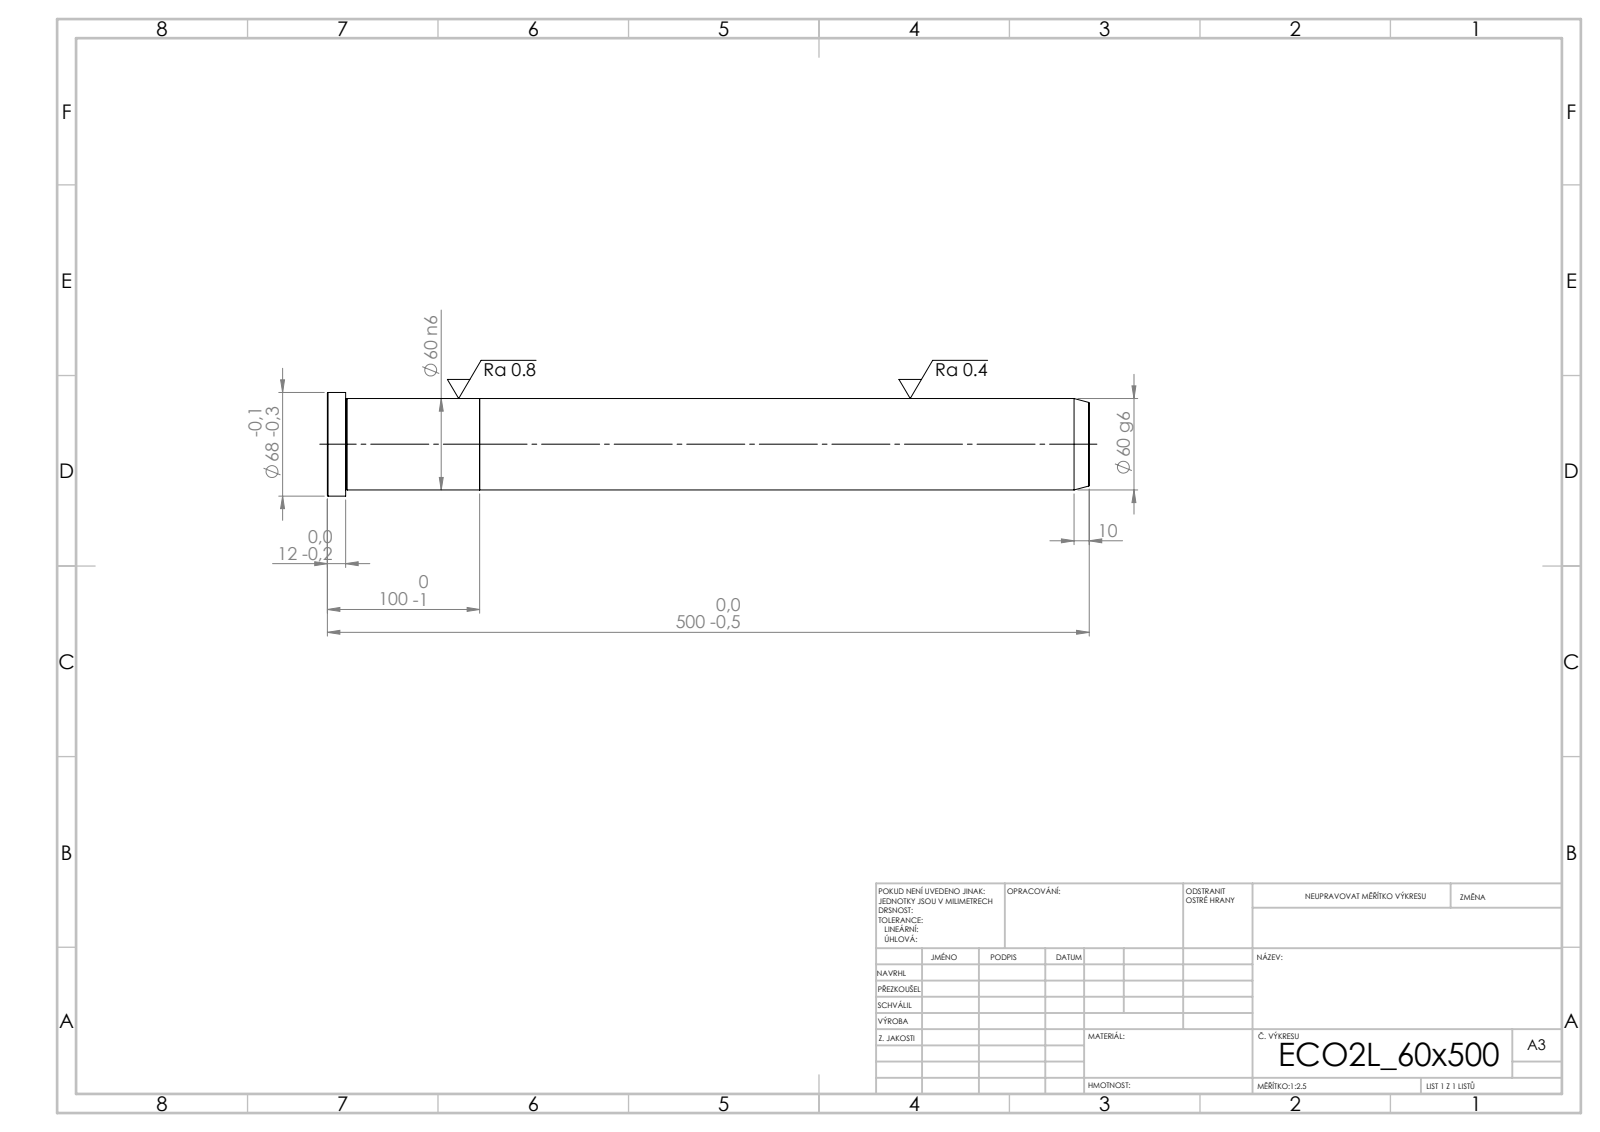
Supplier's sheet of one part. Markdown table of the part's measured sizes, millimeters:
| quantity | value |
| --- | --- |
| STEP written by | SolidWorks 2019 (CONFIG_CONTROL_DESIGN) |
| units | millimeters |
| bodies | 2 solids, 21 faces (5 planar, 6 cylindrical, 10 other) |
| overall size | 500 × 68 × 68 |
| volume | 1 421 000 mm³ |
| surface area | 106 987 mm² |
| round bosses / shafts (diameter × count) | 68 × 1, 60 × 1 |
| main face-to-face distances | 100, 400, 500, 488, 88, 12 |
